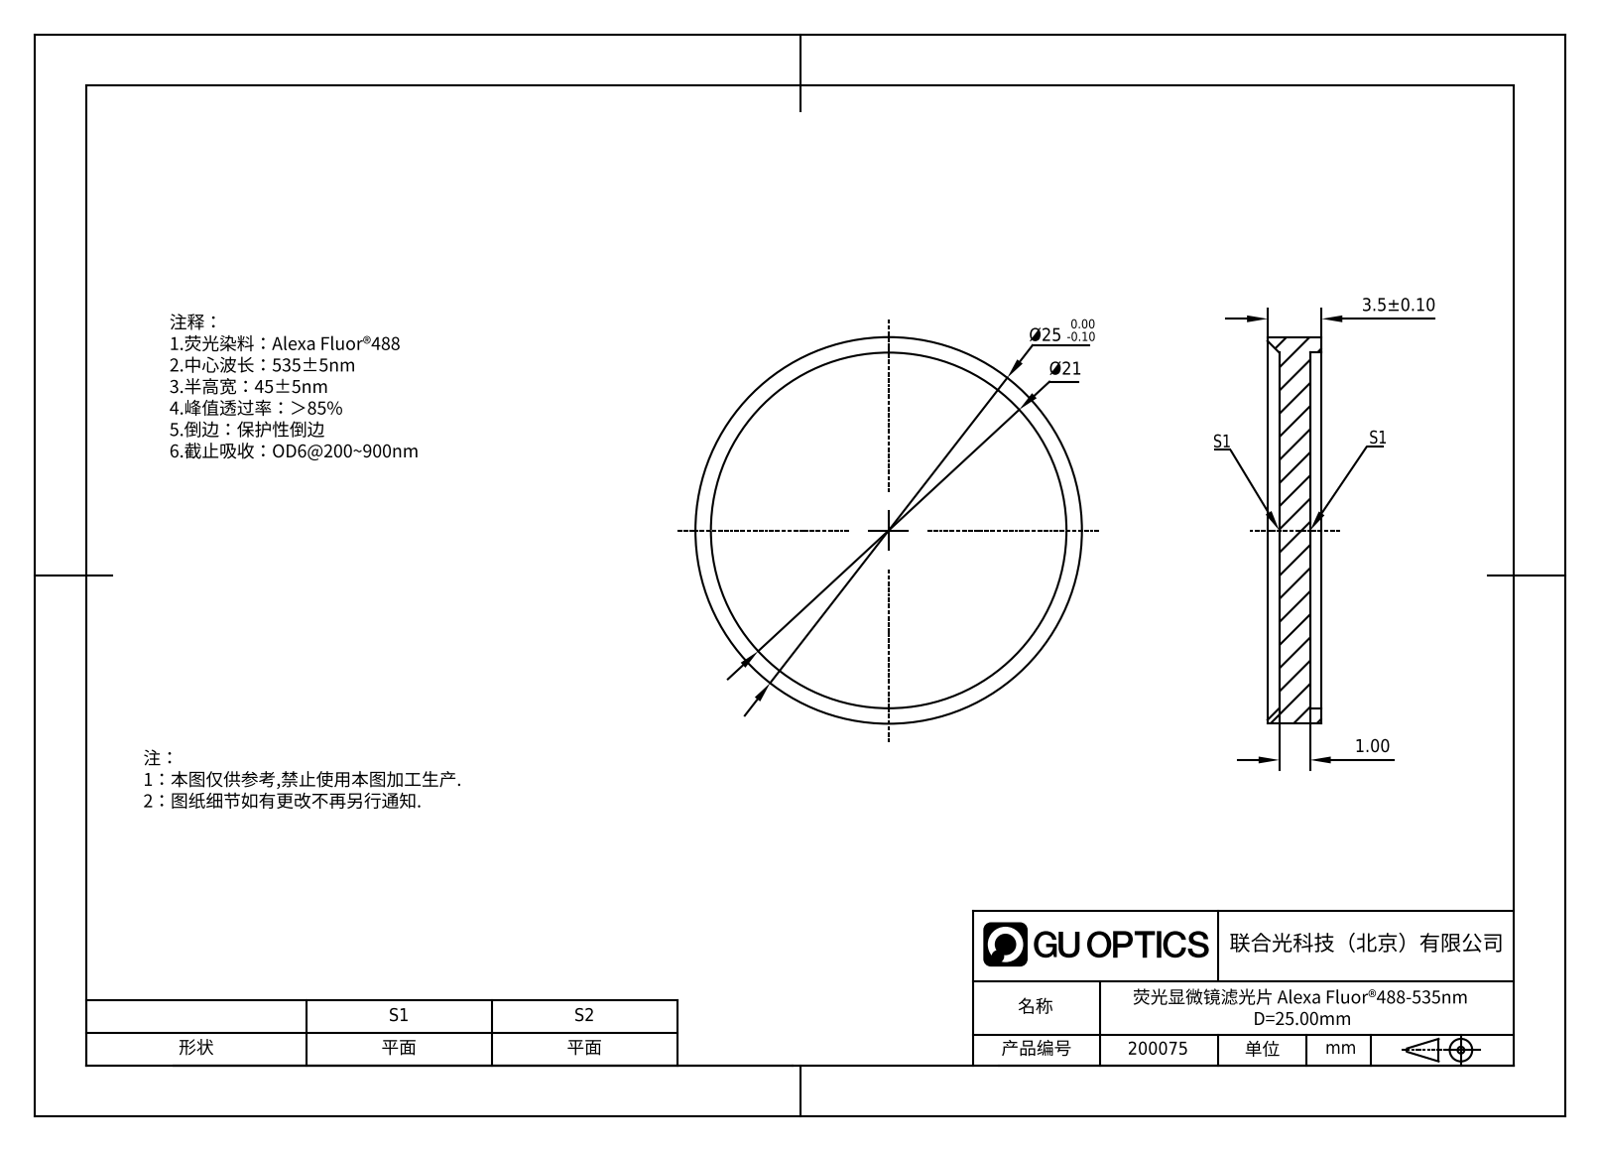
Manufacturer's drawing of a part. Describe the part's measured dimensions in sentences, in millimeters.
The part is named "GNIF-045-535-D25". Its 3-D file was written by "SolidWorks 2022 (AUTOMOTIVE_DESIGN)". It is 1 solid with 10 faces: 4 planar, 4 cylindrical and 2 other. Overall it measures 25 by 25 by 3.5 millimeters. Its volume is 1 074 cubic millimeters and its surface area 1 334 square millimeters. Round holes: 1 of diameter 23. Round bosses or shafts: 1 of diameter 25. The main face-to-face distances are 2, 0.75, 2.75, 3.5.
